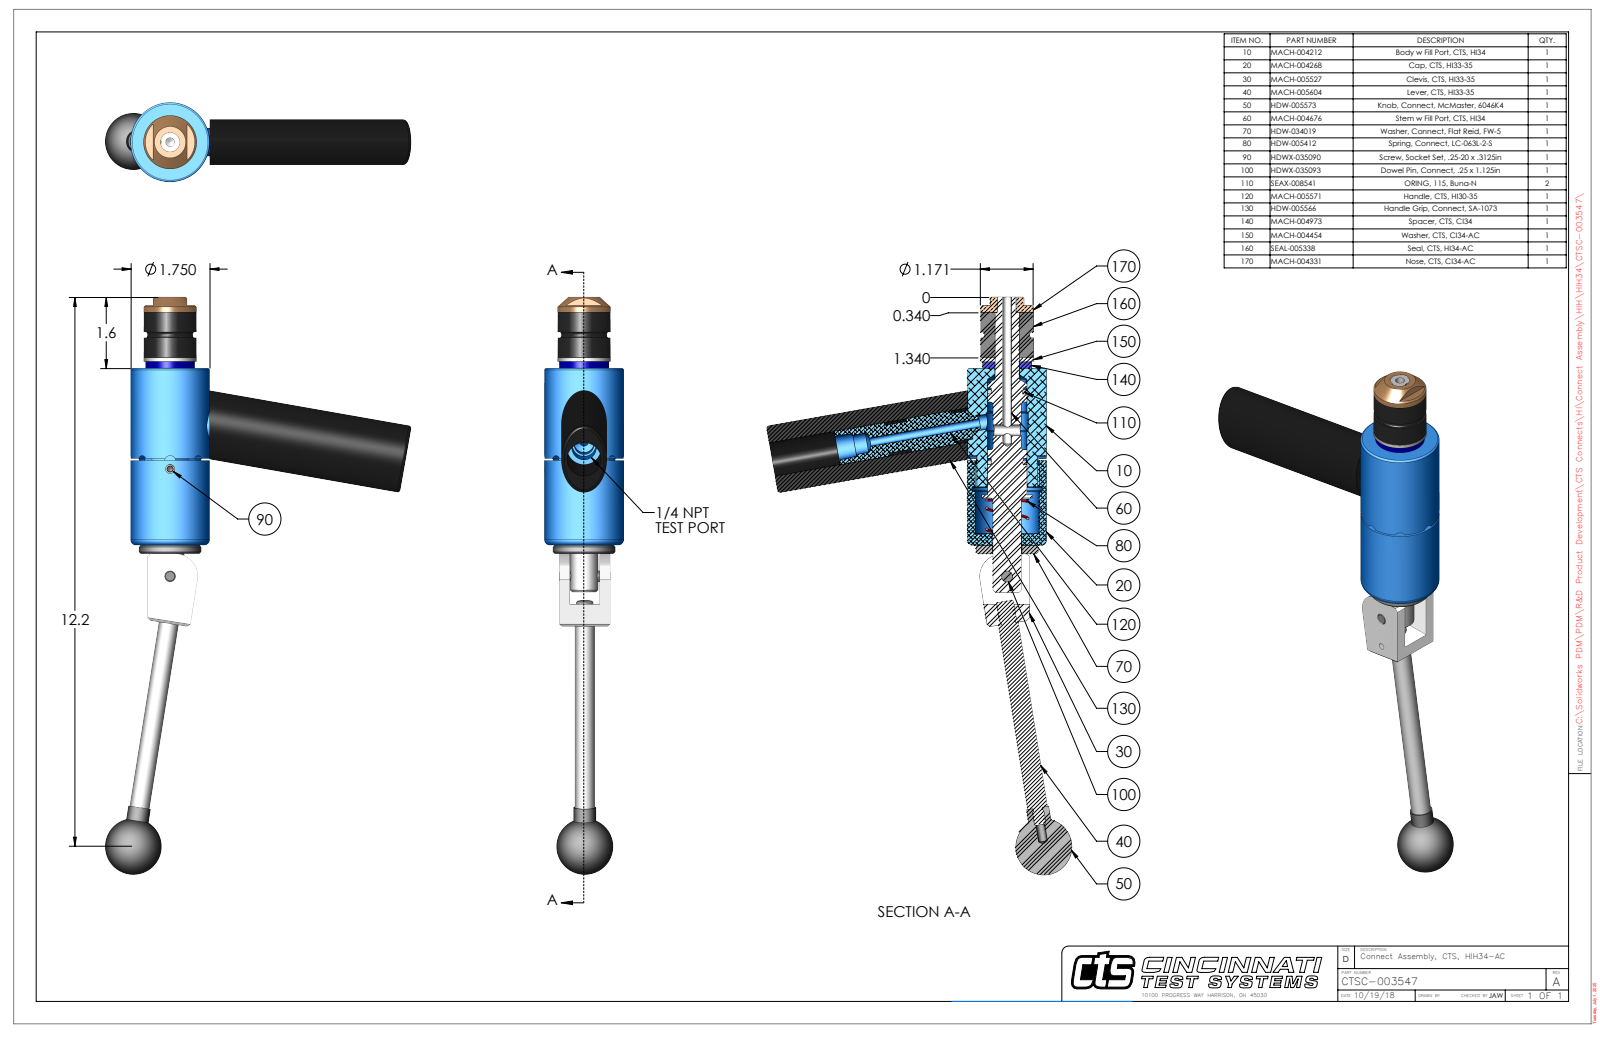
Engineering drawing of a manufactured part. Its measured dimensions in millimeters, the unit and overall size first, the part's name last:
Units: millimetres
Overall size (bounding box): 325 × 171.8 × 44.5
Round holes (diameter × count): ⌀5.1 ×2, ⌀3.8 ×1, ⌀4.7 ×1, ⌀5.2 ×1, ⌀6.3 ×1, ⌀6.4 ×1, ⌀6.4 ×1, ⌀8 ×1, ⌀10.7 ×1, ⌀11.1 ×1, ⌀13.5 ×1, ⌀13.7 ×1
Round bosses / shafts (diameter × count): ⌀12.7 ×2, ⌀11.2 ×2, ⌀6.4 ×2, ⌀44.5 ×1, ⌀35.1 ×1, ⌀29.7 ×1, ⌀27.7 ×1, ⌀19.1 ×1
Partial cylindrical surfaces — rounded edges, fillets, slot ends (radius × count): R3.2 ×4, R0.7 ×2, R4.2 ×1, R4.7 ×1, R8.4 ×1, R12.7 ×1, R17.7 ×1, R20.7 ×1
Main face-to-face distances: 99.6, 31.4, 131, 25.4, 6, 105.6, 27.8, 2.4, 3.6, 103.2
Hole centre spacings: 18.8, 60.4, 79.1
Volume: 300 000 mm³ · Surface area: 75 350 mm²
Bodies: 11 solids, 306 faces (109 planar, 127 cylindrical, 70 other)
Part name (STEP PRODUCT): CTSC-003547
STEP written by: SolidWorks 2023 (AUTOMOTIVE_DESIGN)
